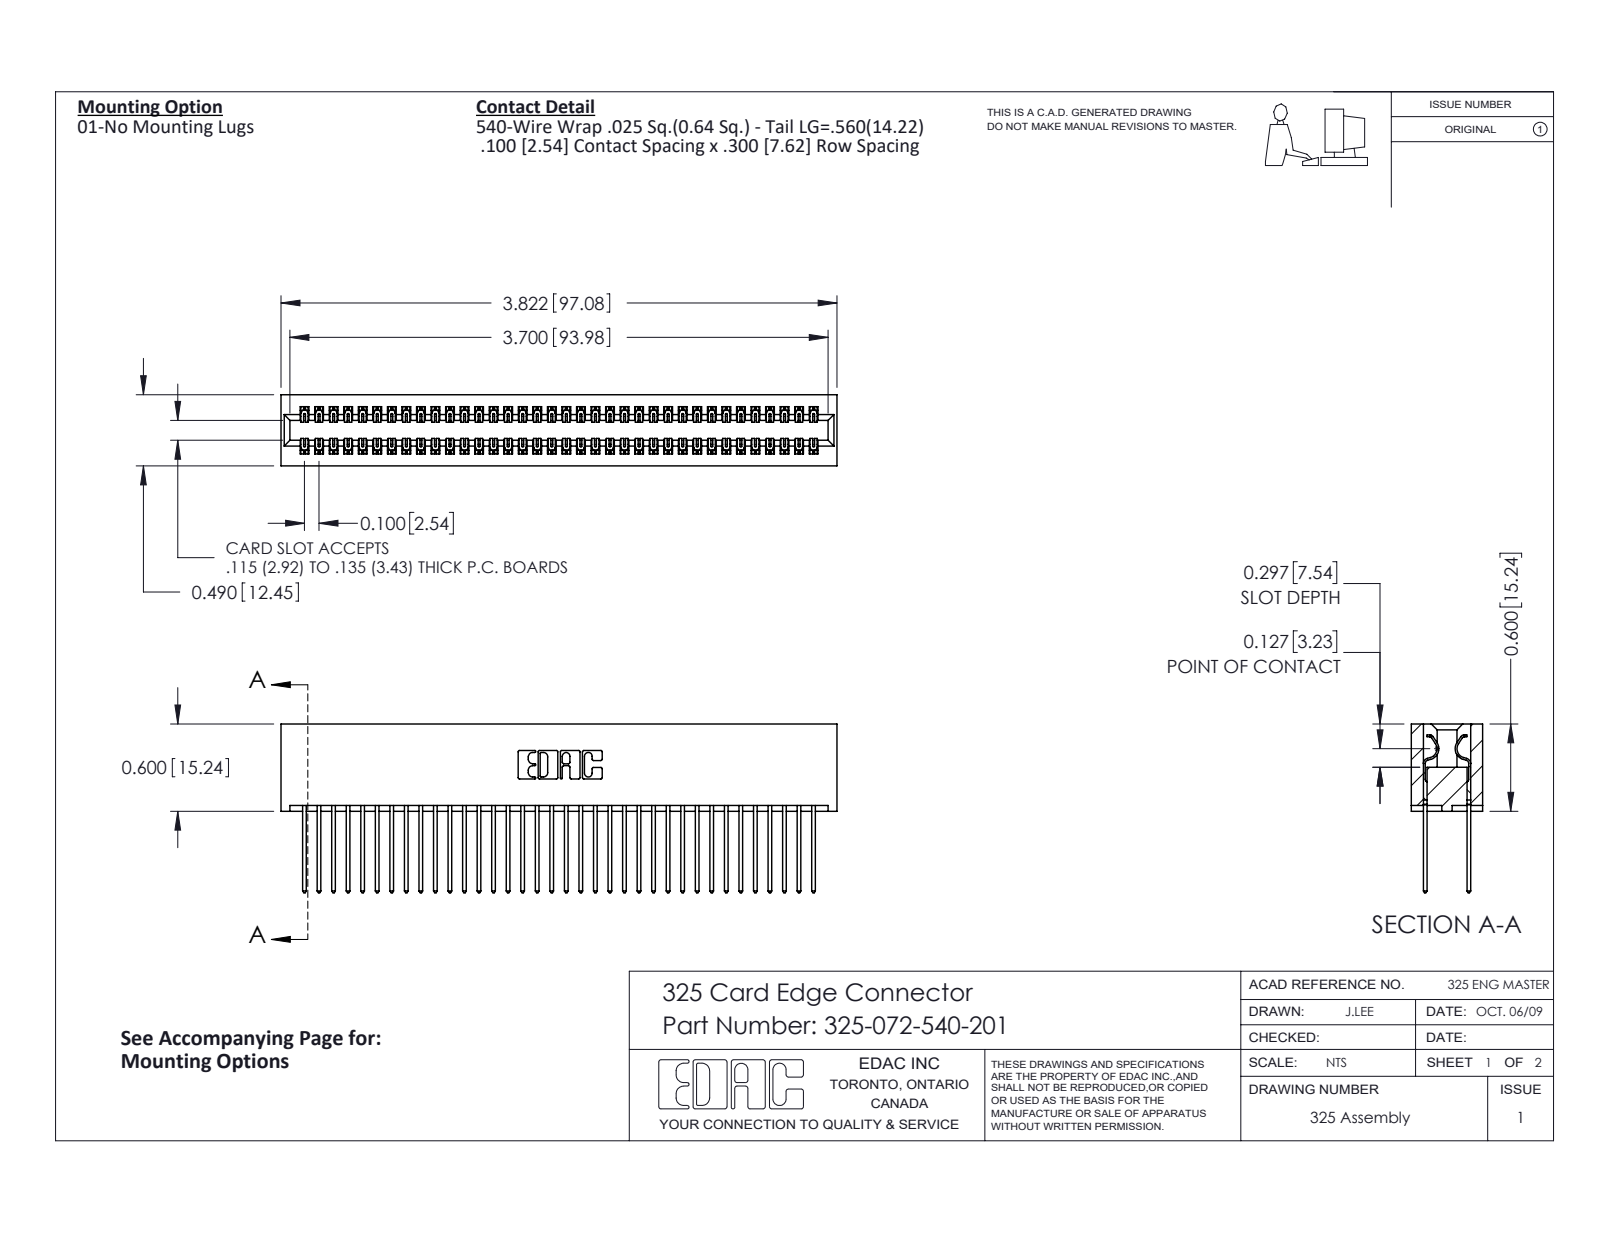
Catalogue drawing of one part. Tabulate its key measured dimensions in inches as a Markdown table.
| quantity | value |
| --- | --- |
| part name | 325-292-001_325-293-140; 325 Part_Lugless; 325-072-540-201 |
| STEP written by | SolidWorks 2016 (CONFIG_CONTROL_DESIGN) |
| units | inches |
| bodies | 73 solids, 3850 faces (2658 planar, 1192 cylindrical, 0 other) |
| overall size | 3.822 × 1.16 × 0.49 |
| volume | 0.815 in³ |
| surface area | 27.88 in² |
| partial cylindrical surfaces (radius × count) | 0.006 × 108, 0.01 × 72, 0.01 × 22, 0.007 × 6, 0.031 × 6, 0.026 × 3, 0.014 × 2, 0.022 × 2 |
| main face-to-face distances | 0.083, 0.407, 0.3, 0.107, 0.383, 0.025, 0.325, 0.49, 0.275, 0.56 |
